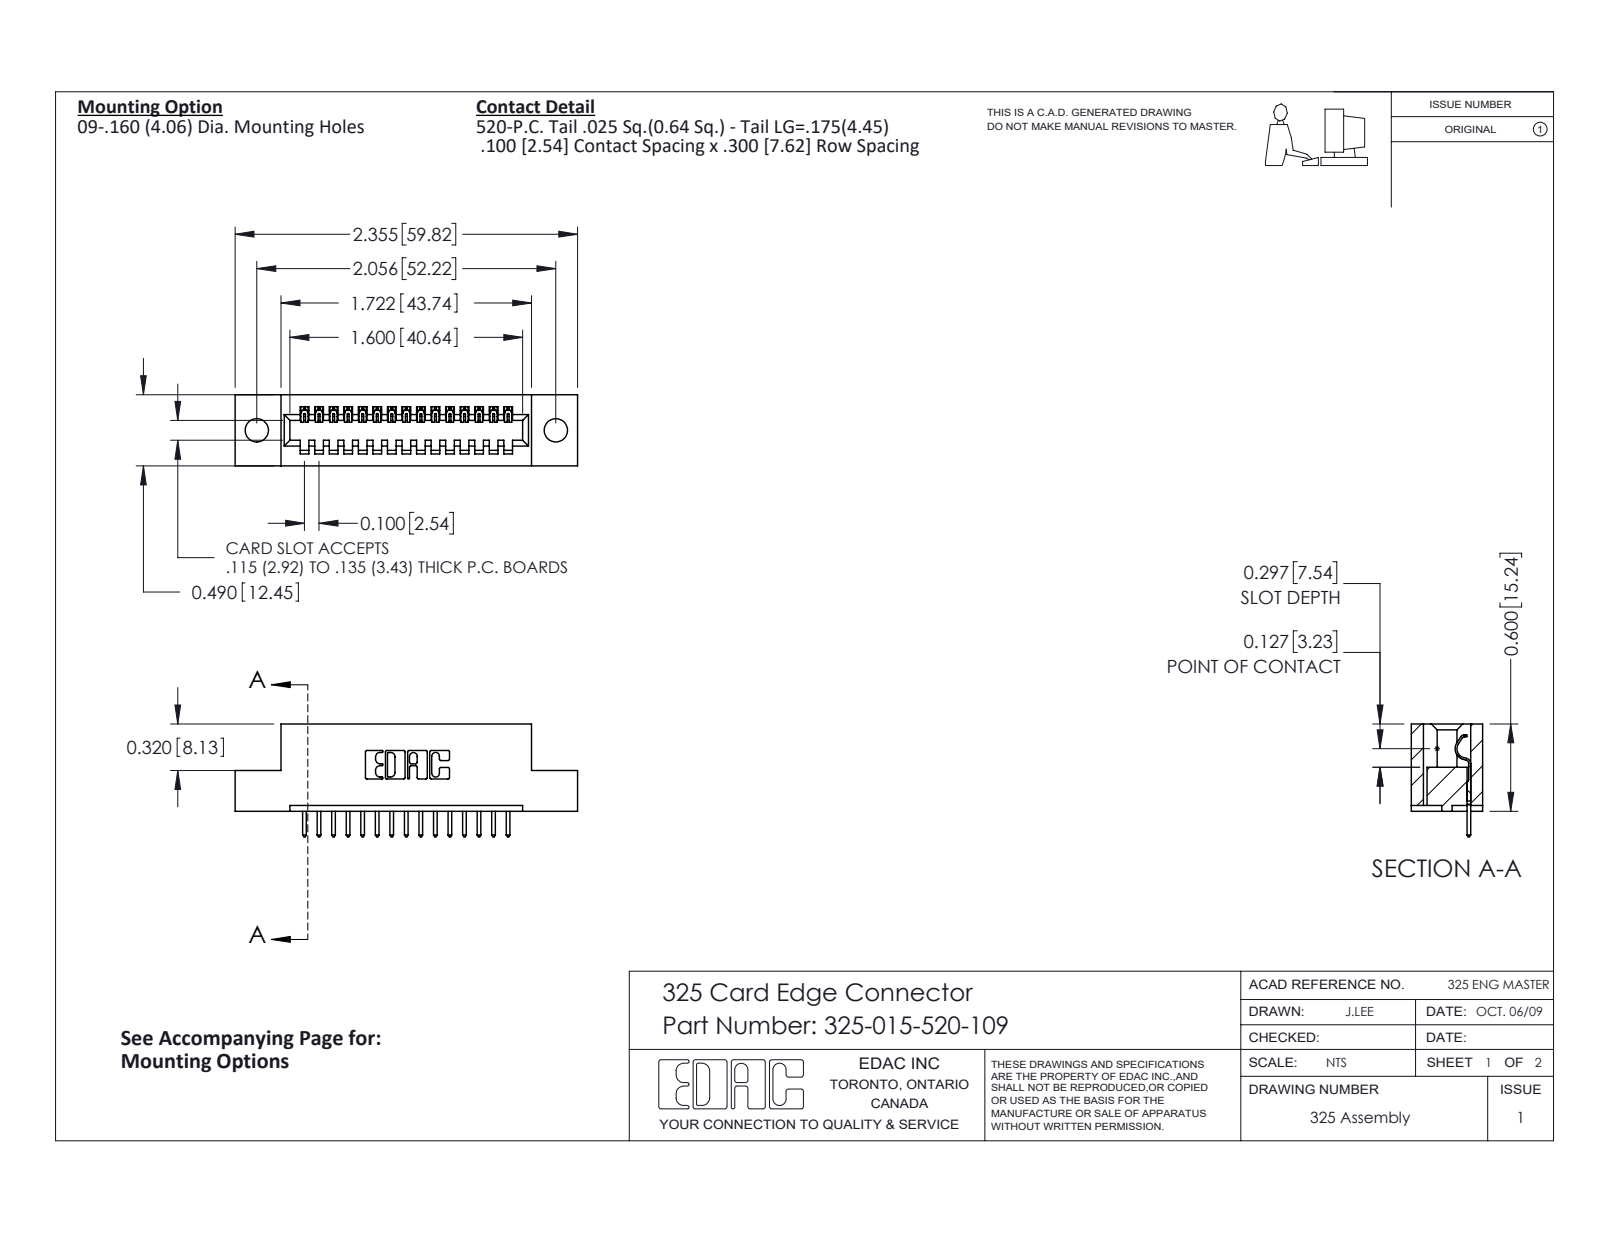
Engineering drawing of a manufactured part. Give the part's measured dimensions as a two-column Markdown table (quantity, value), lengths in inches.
| quantity | value |
| --- | --- |
| part name | 325-292-001_325-293-120; 325-015-520-109; 325 Part_.160 TH |
| STEP written by | SolidWorks 2016 (CONFIG_CONTROL_DESIGN) |
| units | inches |
| bodies | 16 solids, 984 faces (700 planar, 284 cylindrical, 0 other) |
| overall size | 2.355 × 0.775 × 0.49 |
| volume | 0.434 in³ |
| surface area | 10.93 in² |
| round holes (diameter × count) | 0.16 × 2 |
| partial cylindrical surfaces (radius × count) | 0.006 × 30, 0.01 × 30, 0.01 × 22, 0.007 × 6, 0.031 × 6, 0.026 × 3, 0.014 × 1, 0.022 × 1 |
| main face-to-face distances | 0.083, 0.407, 0.49, 0.3, 0.04, 0.1, 0.107, 0.383, 0.025, 0.6 |
| hole center spacings | 2.056 |
